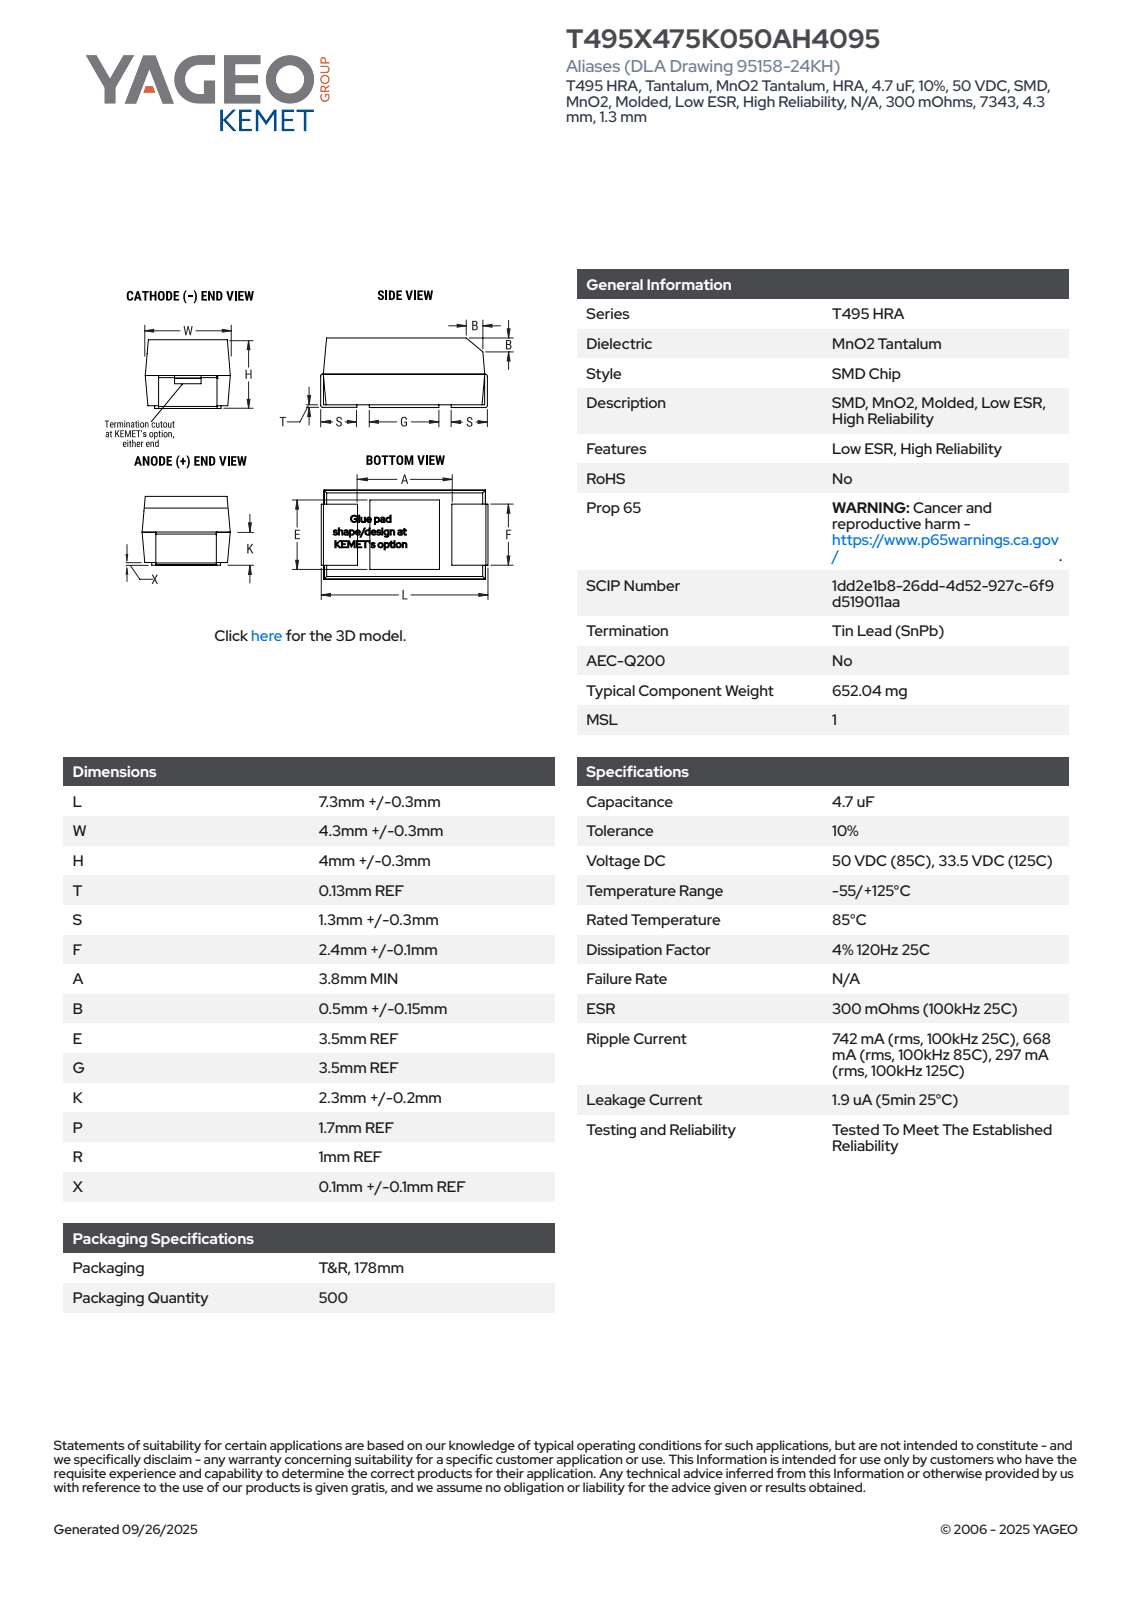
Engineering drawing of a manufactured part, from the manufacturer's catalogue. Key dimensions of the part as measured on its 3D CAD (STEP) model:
Part name (STEP PRODUCT): CTSM_Case_Anode_30; CTSM_Case_Bottom_30; CTSM_Case_Cathode_30; CTSM_Case_Top_30 (+1 more)
STEP written by: SolidWorks 2014 (AUTOMOTIVE_DESIGN)
Units: millimetres
Bodies: 7 solids, 100 faces (95 planar, 5 cylindrical, 0 other)
Overall size (bounding box): 7.6 × 4.6 × 4.3
Volume: 134 mm³ · Surface area: 260 mm²
Main face-to-face distances: 2, 4.58, 2.17, 4.17, 7.31, 7.47, 2.27, 4.27, 2.3, 4.3
